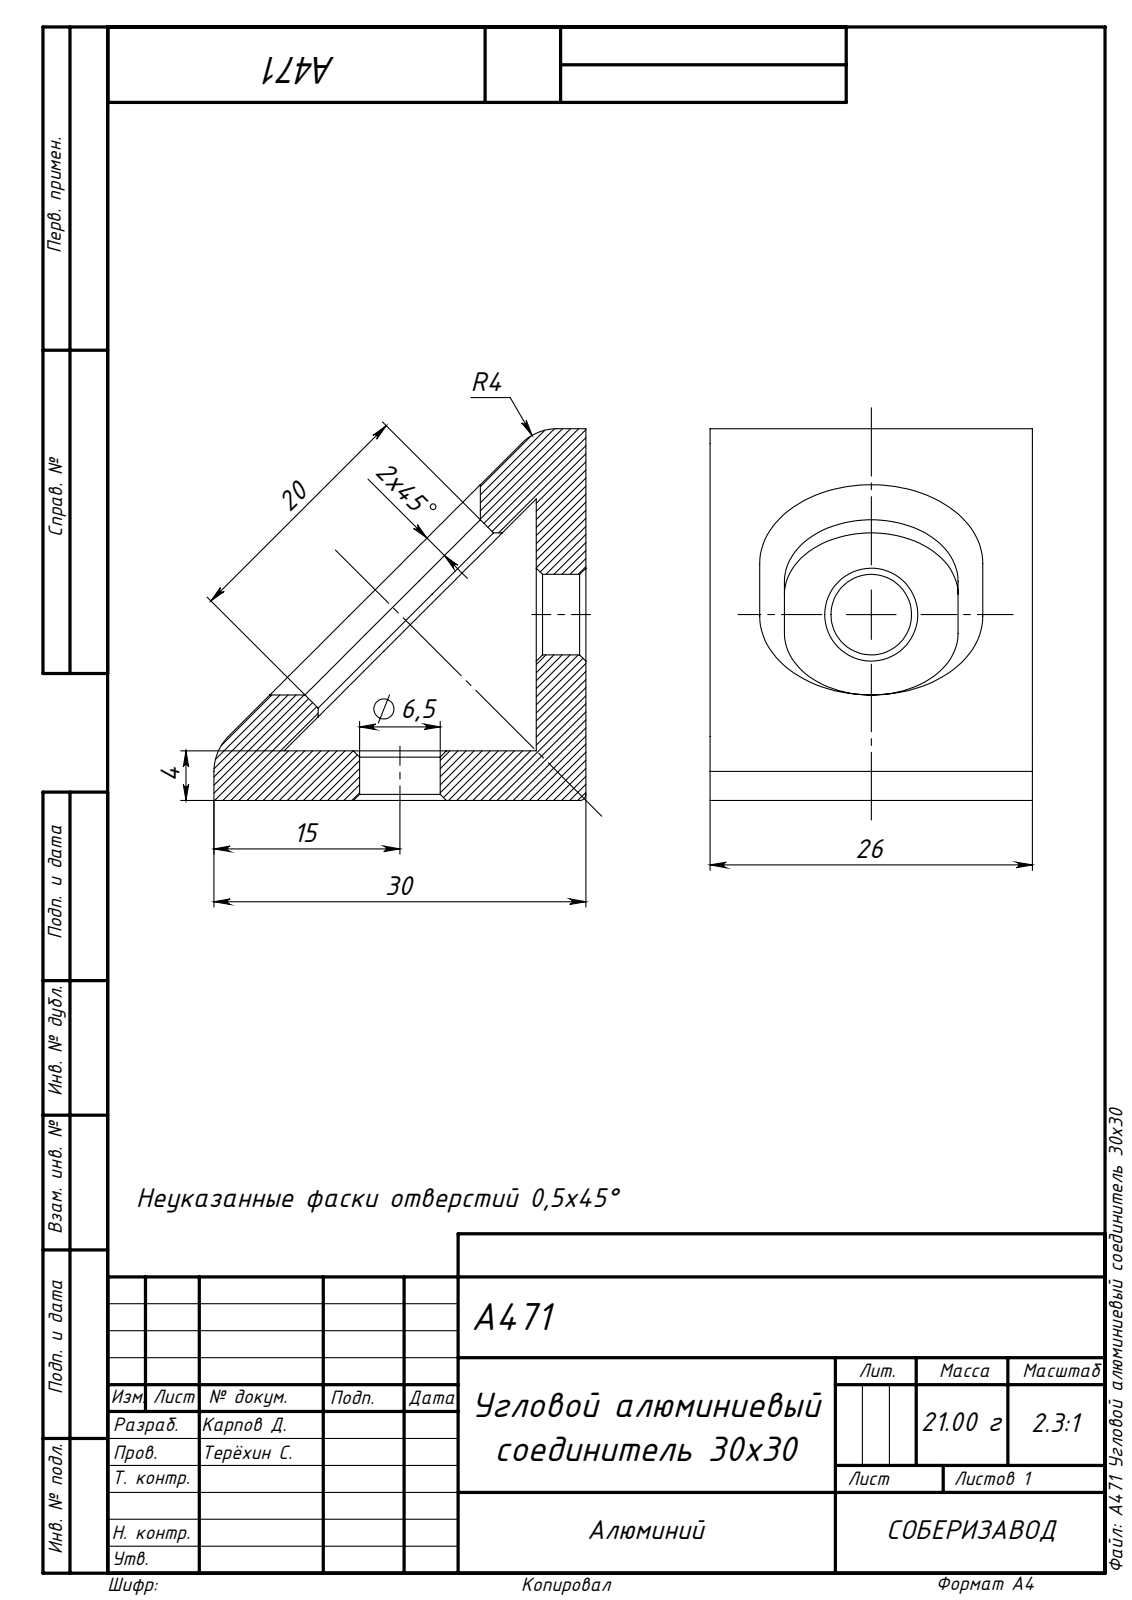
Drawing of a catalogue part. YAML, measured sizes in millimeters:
part_name: "A471 Угловой алюминиевый соединитель 30х30"
step_written_by: "SolidWorks 2021 (AUTOMOTIVE_DESIGN)"
units: millimeters
bodies: {solids: 1, faces: 40, planar: 16, cylindrical: 10, other: 14}
overall_size: [30, 30, 26]
volume: 7857
surface_area: 4904
round_holes:
  - {diameter: 6.5, count: 2}
partial_cylinders:
  - {radius: 4, count: 2}
  - {radius: 7, count: 2}
  - {radius: 0.5, count: 1}
face_to_face_distances: [4, 26, 30, 6, 20, 14, 8.84, 8.83]
